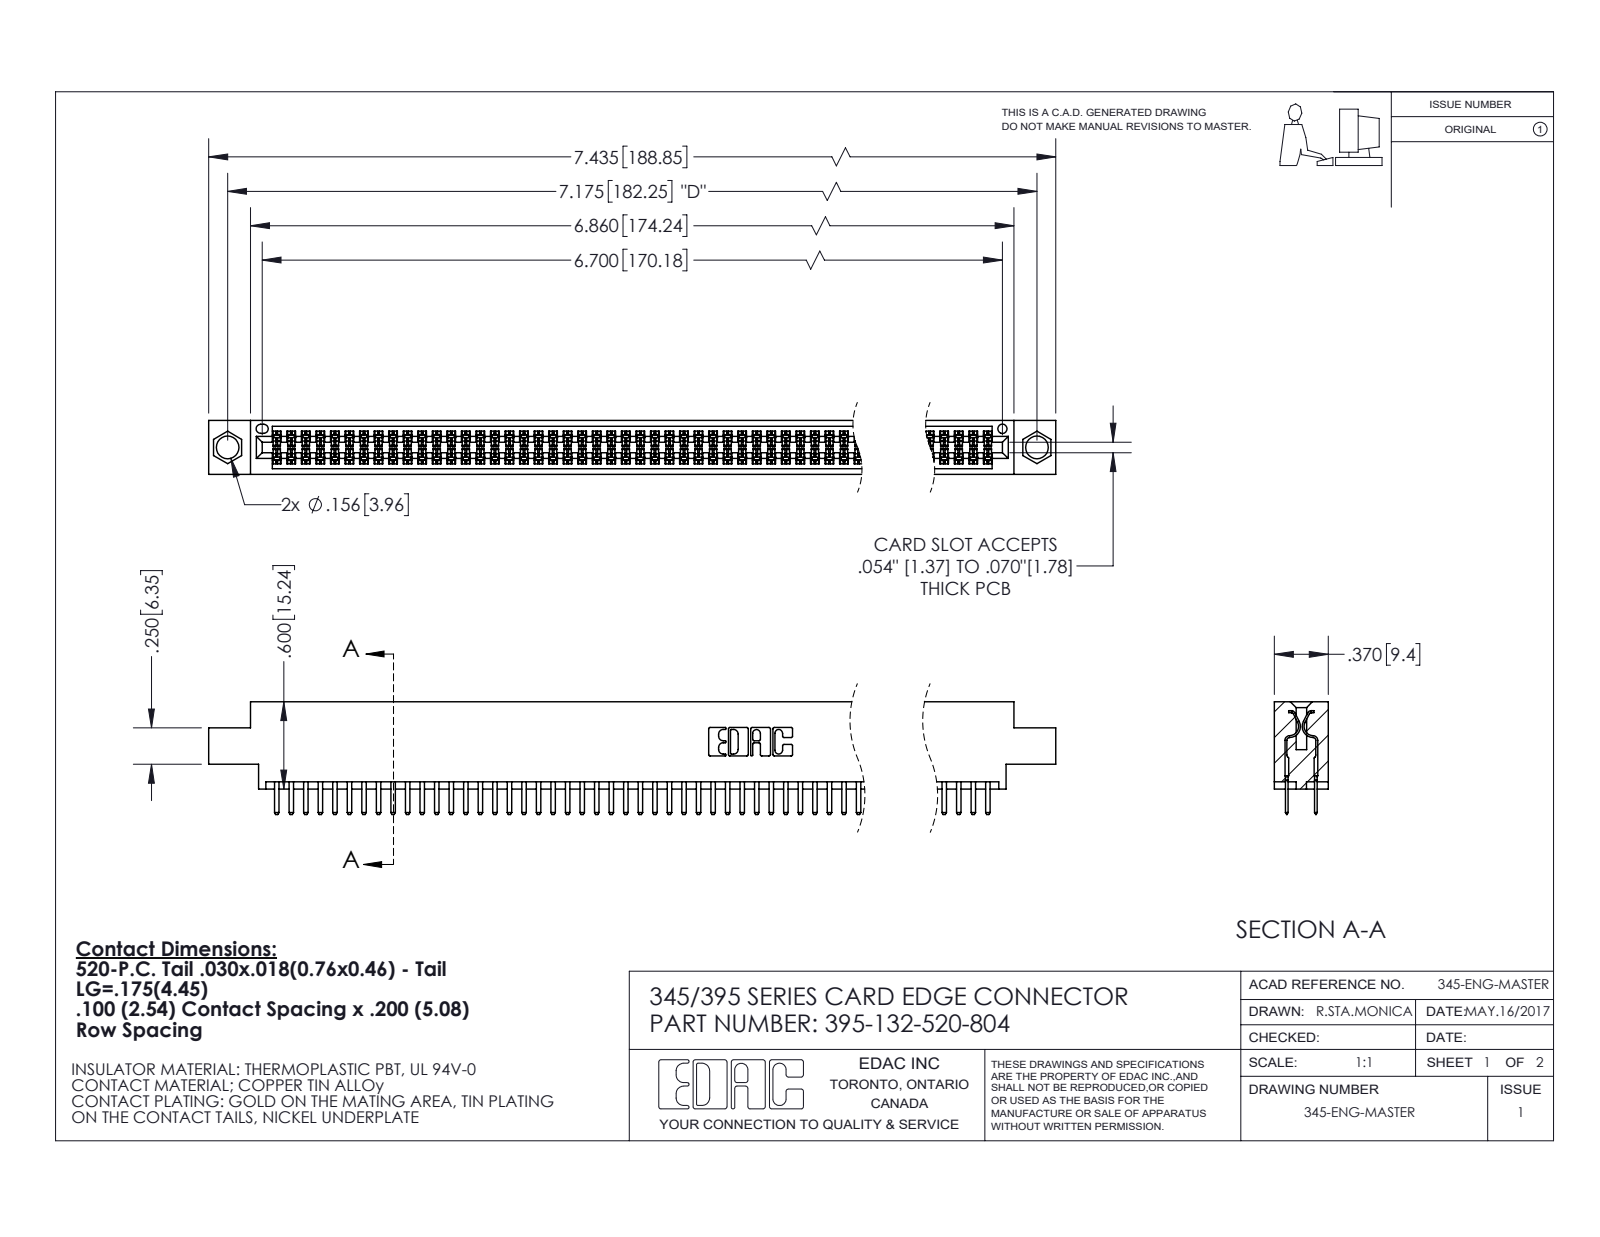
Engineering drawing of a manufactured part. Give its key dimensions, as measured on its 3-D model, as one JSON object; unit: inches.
{"part_name": "345-292-001_345-293-120; 395-132-520-804; 345 Part_0.170 Offset - 0.156 Dia-TI", "step_written_by": "SolidWorks 2020 (CONFIG_CONTROL_DESIGN)", "units": "inches", "bodies": {"solids": 133, "faces": 7272, "planar": 4718, "cylindrical": 2554, "other": 0}, "overall_size": [7.435, 0.775, 0.37], "volume_in3": 1.116, "surface_area_in2": 42.43, "round_holes": [[0.156, 2], [0.064, 1]], "partial_cylinders_radius": [[0.006, 264], [0.01, 136], [0.01, 22], [0.007, 6], [0.031, 6], [0.026, 3], [0.014, 2], [0.019, 2]], "face_to_face_distances": [0.072, 0.298, 0.2, 0.37, 0.098, 0.272, 0.025, 0.225, 0.022, 0.072], "hole_center_spacings": [0.27, 6.939, 7.175]}
